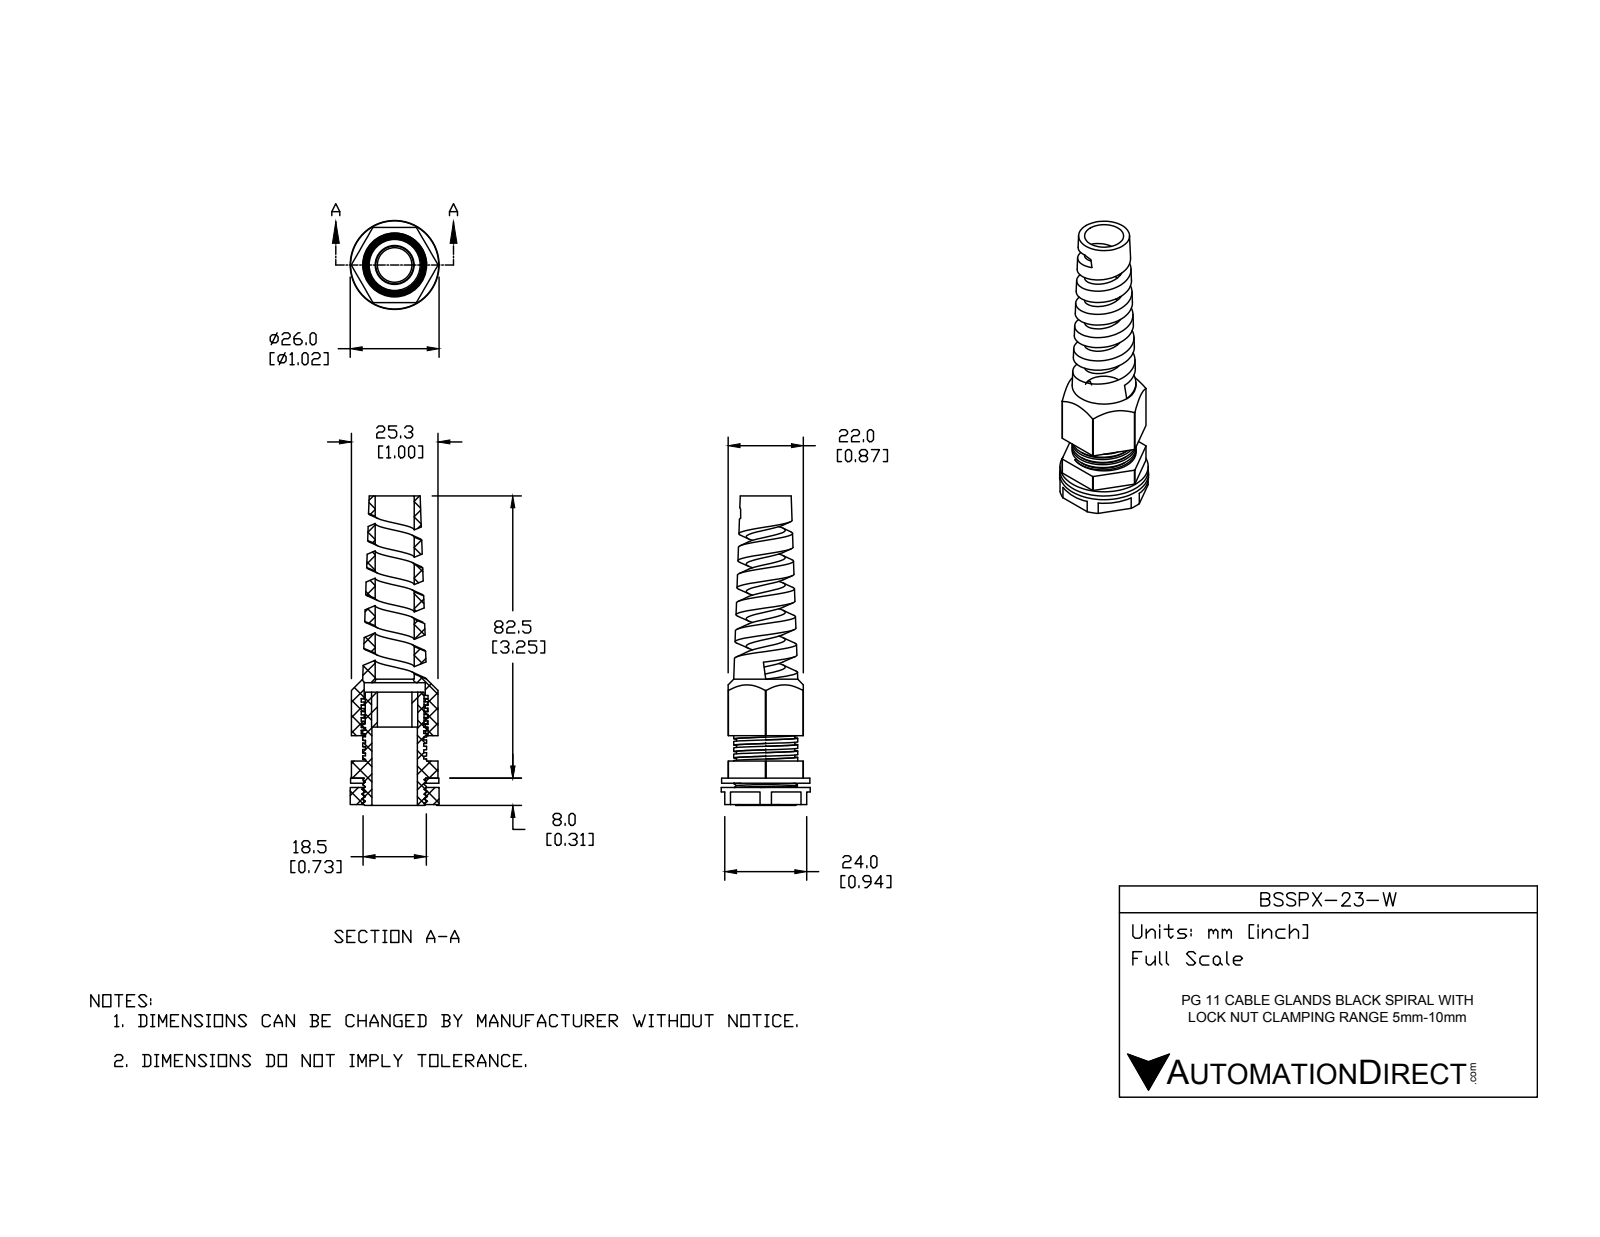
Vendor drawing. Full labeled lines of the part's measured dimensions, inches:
Part name (STEP PRODUCT): BSSPX-23-W
STEP written by: SolidWorks 2015 (CONFIG_CONTROL_DESIGN)
Units: inches
Bodies: 5 solids, 228 faces (103 planar, 91 cylindrical, 34 other)
Overall size (bounding box): 3.563 × 1.024 × 1.024
Volume: 0.792 in³ · Surface area: 24.28 in²
Round holes (diameter × count): ⌀0.398 ×1, ⌀0.449 ×1, ⌀0.524 ×1, ⌀0.531 ×1, ⌀0.702 ×1, ⌀0.704 ×1, ⌀0.717 ×1
Round bosses / shafts (diameter × count): ⌀1.024 ×1, ⌀1.016 ×1, ⌀0.736 ×1, ⌀0.728 ×1, ⌀0.677 ×1
Partial cylindrical surfaces — rounded edges, fillets, slot ends (radius × count): R0.498 ×1
Main face-to-face distances: 0.866, 0.039, 0.197, 0.295, 0.098, 0.256, 0.059, 0.02, 0.236, 0.906
